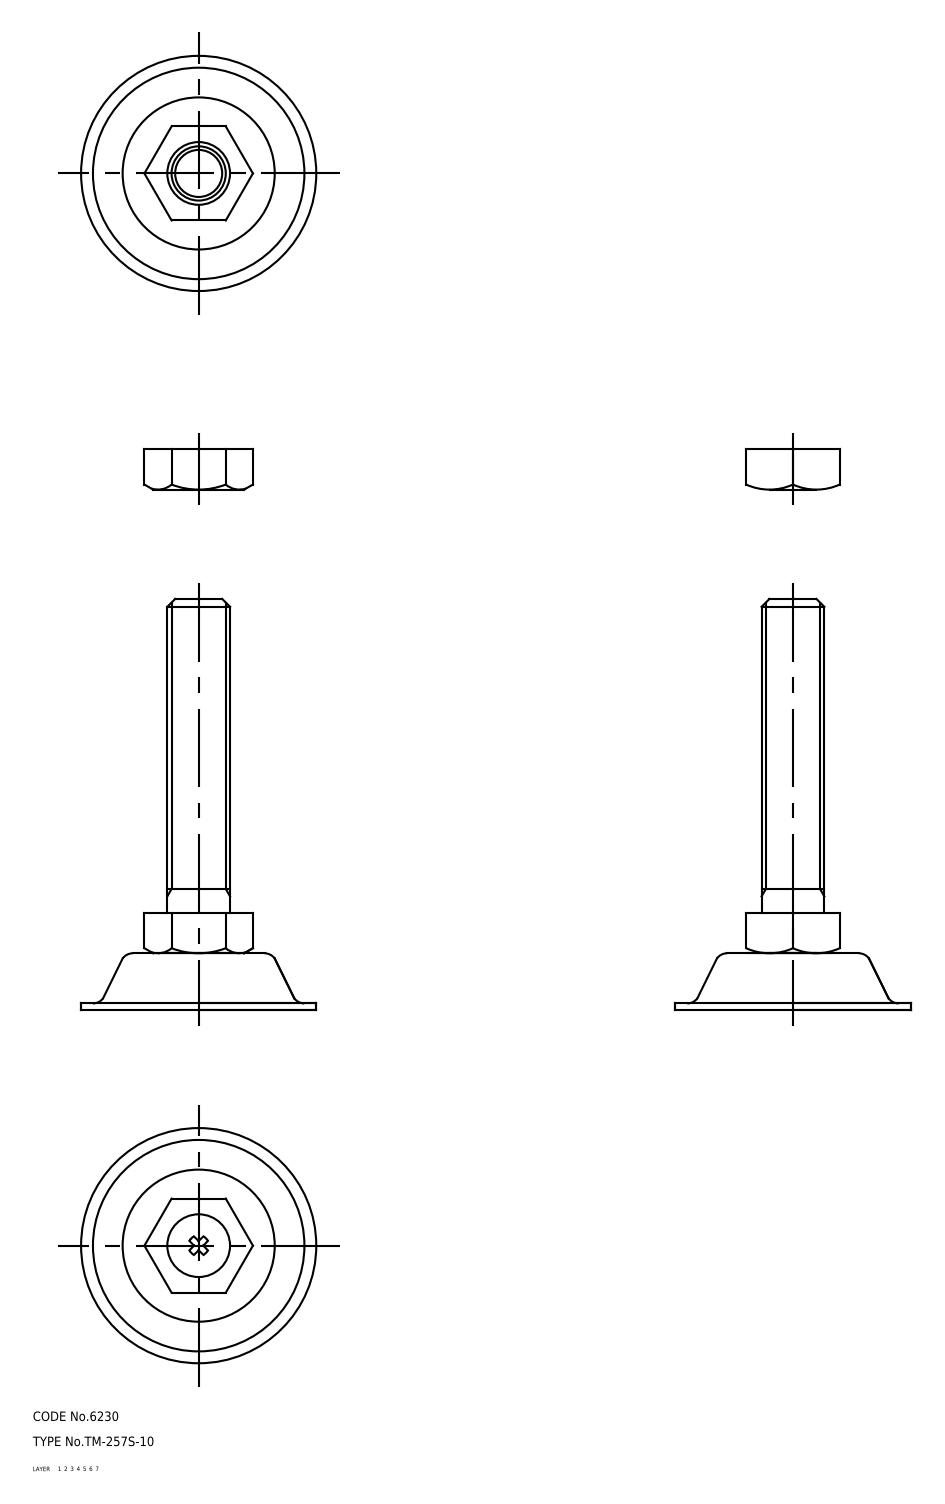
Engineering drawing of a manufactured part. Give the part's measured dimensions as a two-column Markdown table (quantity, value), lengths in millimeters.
| quantity | value |
| --- | --- |
| part name | nut; foot; bolt; TM_257S_10_10103_36 |
| STEP written by | CADfix (AUTOMOTIVE_DESIGN) |
| units | millimeters |
| bodies | 4 solids, 83 faces (0 planar, 0 cylindrical, 83 other) |
| overall size | 131 × 75 × 75 |
| volume | 69 518 mm³ |
| surface area | 28 033 mm² |
